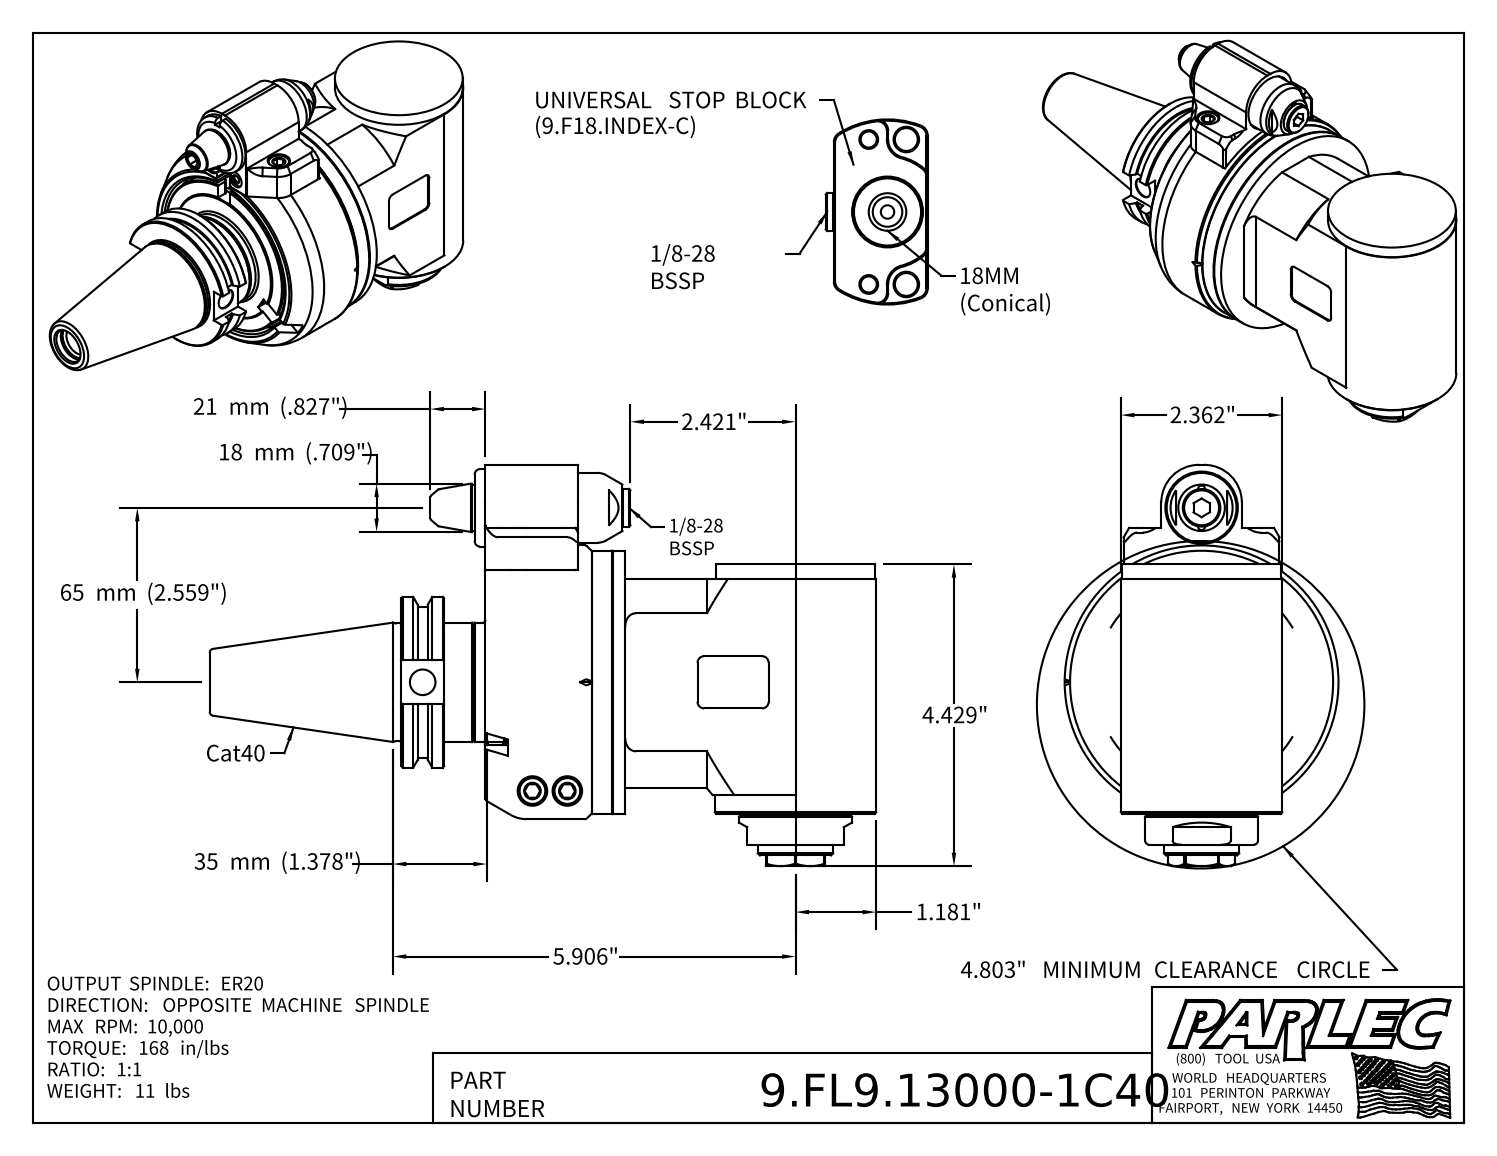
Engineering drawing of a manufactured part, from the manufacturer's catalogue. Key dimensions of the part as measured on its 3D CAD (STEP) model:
Part name (STEP PRODUCT): 9.FL9.13000-1C40; 9_FL9_13000; 9_GA15C_446 (Type 1, Cat40, 65mm, conical)
STEP written by: Autodesk Inventor 2025 (AUTOMOTIVE_DESIGN)
Units: inches
Bodies: 27 solids, 730 faces (308 planar, 204 cylindrical, 218 other)
Overall size (bounding box): 9.774 × 5.886 × 4.016
Volume: 54.45 in³ · Surface area: 254 in²
Round holes (diameter × count): ⌀0.197 ×7, ⌀0.165 ×6, ⌀0.126 ×4, ⌀0.13 ×4, ⌀0.236 ×3, ⌀0.315 ×3, ⌀0.807 ×3, ⌀0.102 ×2, ⌀0.256 ×2, ⌀0.266 ×2, ⌀0.409 ×2, ⌀0.433 ×2
Round bosses / shafts (diameter × count): ⌀0.394 ×5, ⌀0.236 ×4, ⌀0.157 ×4, ⌀0.866 ×2, ⌀0.709 ×2, ⌀0.197 ×2, ⌀4.016 ×1, ⌀3.858 ×1
Partial cylindrical surfaces — rounded edges, fillets, slot ends (radius × count): R0.039 ×14, R0.118 ×6, R0.098 ×4, R0.157 ×4, R0.02 ×2, R0.315 ×2, R0.551 ×2, R0.492 ×1
Main face-to-face distances: 0.02, 2.362, 0.276, 0.492, 1.555, 0.079, 0.039, 2.047, 0.335, 0.65
Hole centre spacings: 0.325, 0.459, 0.276, 0.472, 0.504, 0.65, 0.74, 0.838
